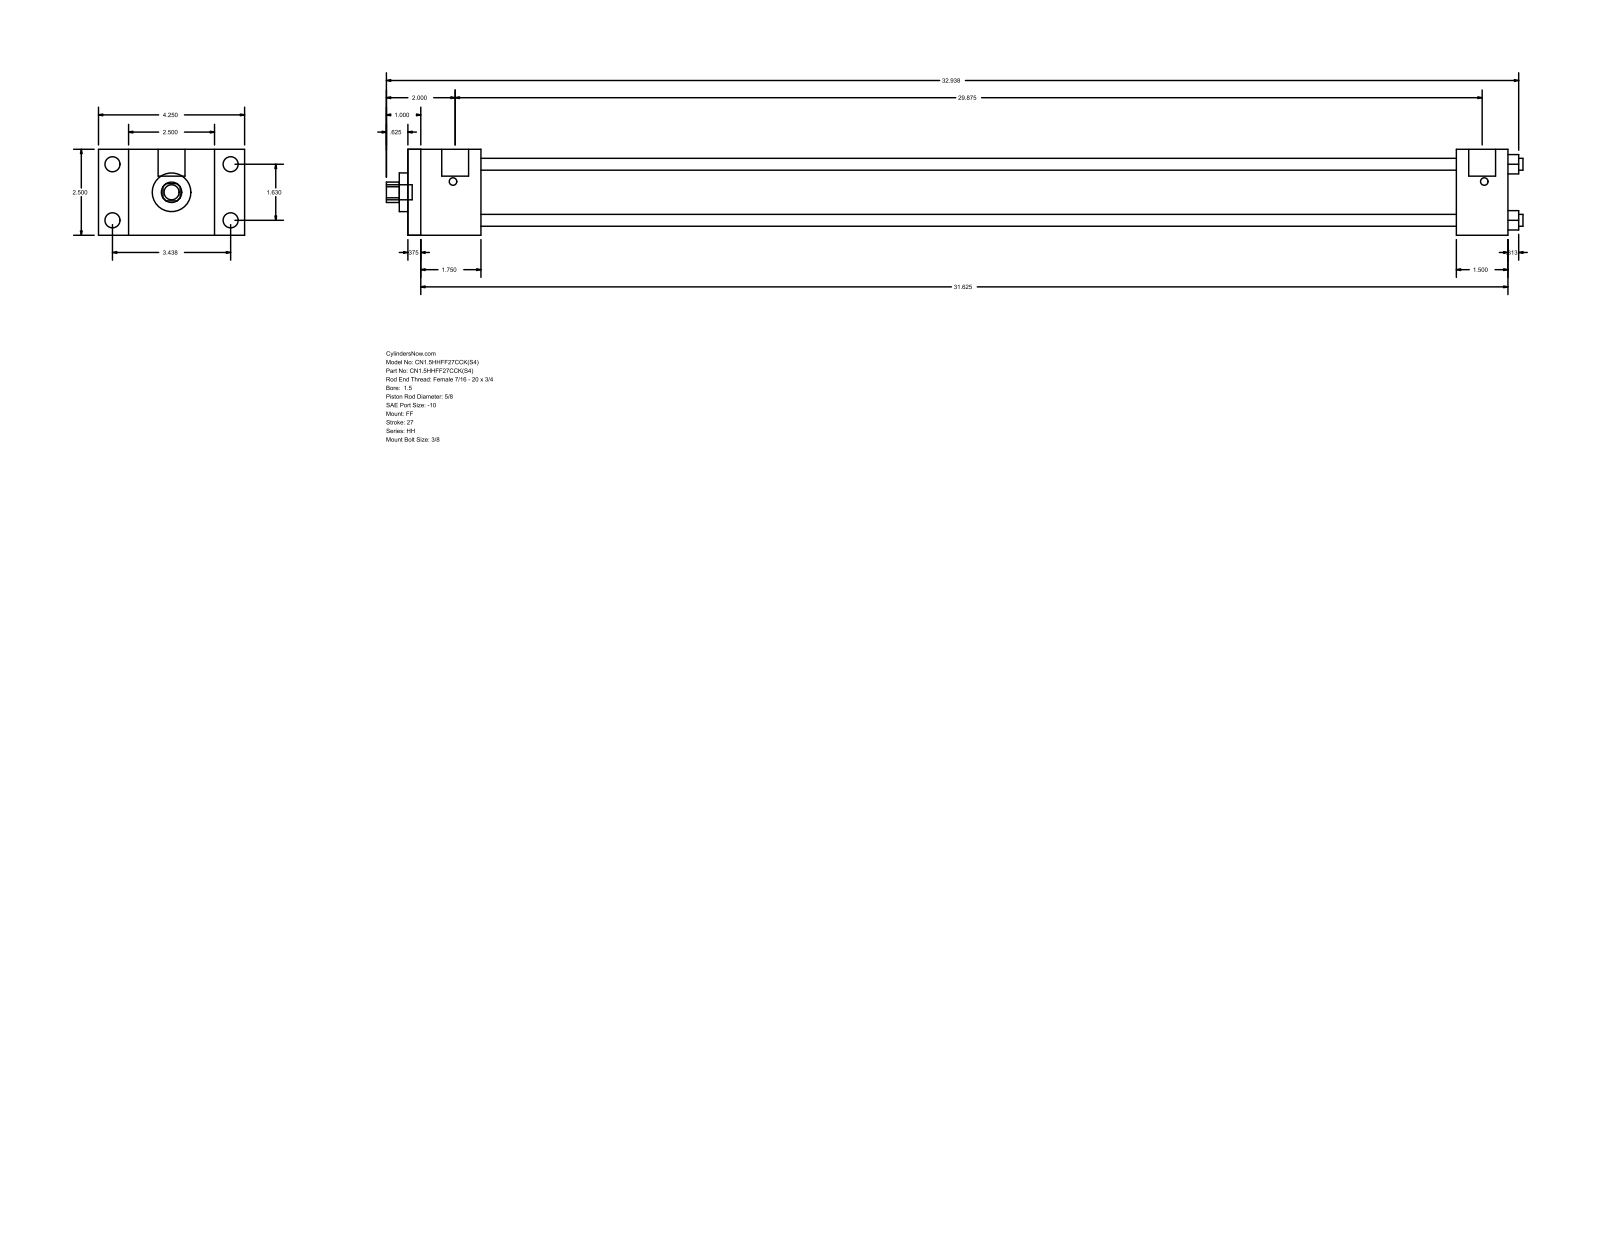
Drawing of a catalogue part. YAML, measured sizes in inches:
part_name: "HH_FF__0150_0.625"
step_written_by: "GSSL Pune (CONFIG_CONTROL_DESIGN)"
units: inches
bodies: {solids: 0, faces: 92, planar: 64, cylindrical: 28, other: 0}
overall_size: [33.063, 4.25, 2.5]
round_holes:
  - {diameter: 0.345, count: 4}
  - {diameter: 0.625, count: 1}
  - {diameter: 1.125, count: 1}
  - {diameter: 1.75, count: 1}
round_bosses_or_shafts:
  - {diameter: 0.438, count: 4}
  - {diameter: 0.219, count: 4}
  - {diameter: 0.781, count: 2}
  - {diameter: 0.437, count: 1}
partial_cylinders:
  - {radius: 0.297, count: 1}
face_to_face_distances: [2.5, 32, 0.375, 31.625, 2.125, 1.75, 29.875, 30.5, 30.125, 28.375]
hole_center_spacings: [1.152, 1.63, 2.305]
